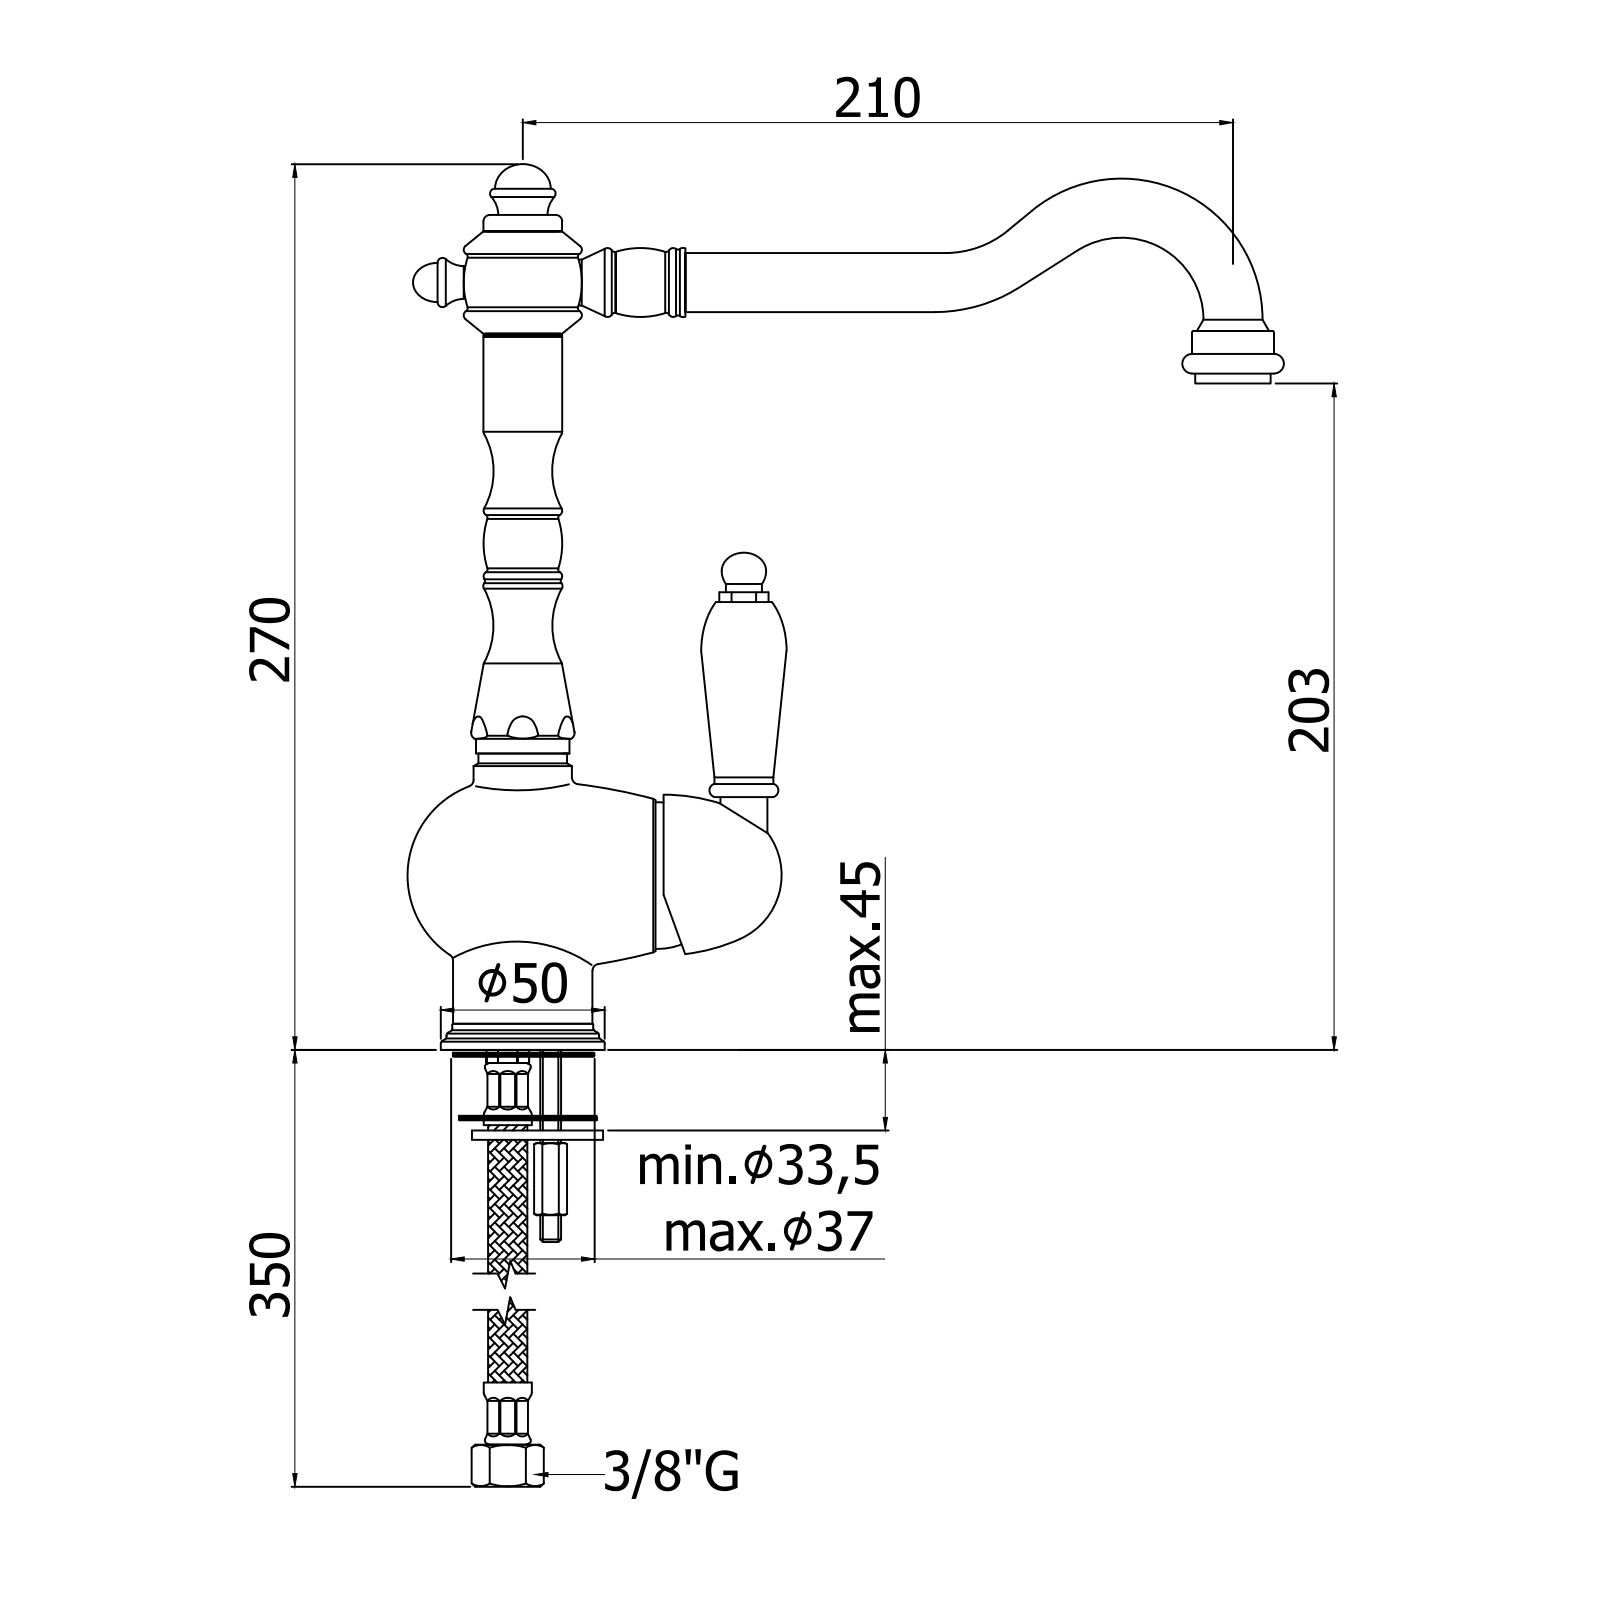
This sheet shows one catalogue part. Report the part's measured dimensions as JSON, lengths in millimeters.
{"part_name": "FME181CR", "step_written_by": "CREO PARAMETRIC BY PTC INC, 2020044 (CONFIG_CONTROL_DESIGN)", "units": "millimeters", "bodies": {"solids": 1, "faces": 457, "planar": 105, "cylindrical": 121, "other": 231}, "overall_size": [274.3, 264.73, 121.91], "volume_mm3": 363553, "surface_area_mm2": 88807, "round_holes": [[5.5, 3], [9, 3], [5.25, 2], [6.5, 2], [7, 2], [8, 2], [11, 2], [3, 1], [4.2, 1], [10, 1], [12.75, 1], [14.5, 1]], "round_bosses_or_shafts": [[22, 2], [18, 2], [50, 1], [46.5, 1], [43, 1], [37.4, 1], [30, 1], [26.8, 1]], "partial_cylinders_radius": [[2.75, 1], [5.25, 1], [10, 1], [24, 1], [25, 1]], "face_to_face_distances": [51, 50.98, 6, 7.5, 93, 87, 4, 79.5, 5, 76.5], "hole_center_spacings": [7.82, 8.6, 9.6, 12.26, 13.04, 13.46, 14.33, 15.62]}
